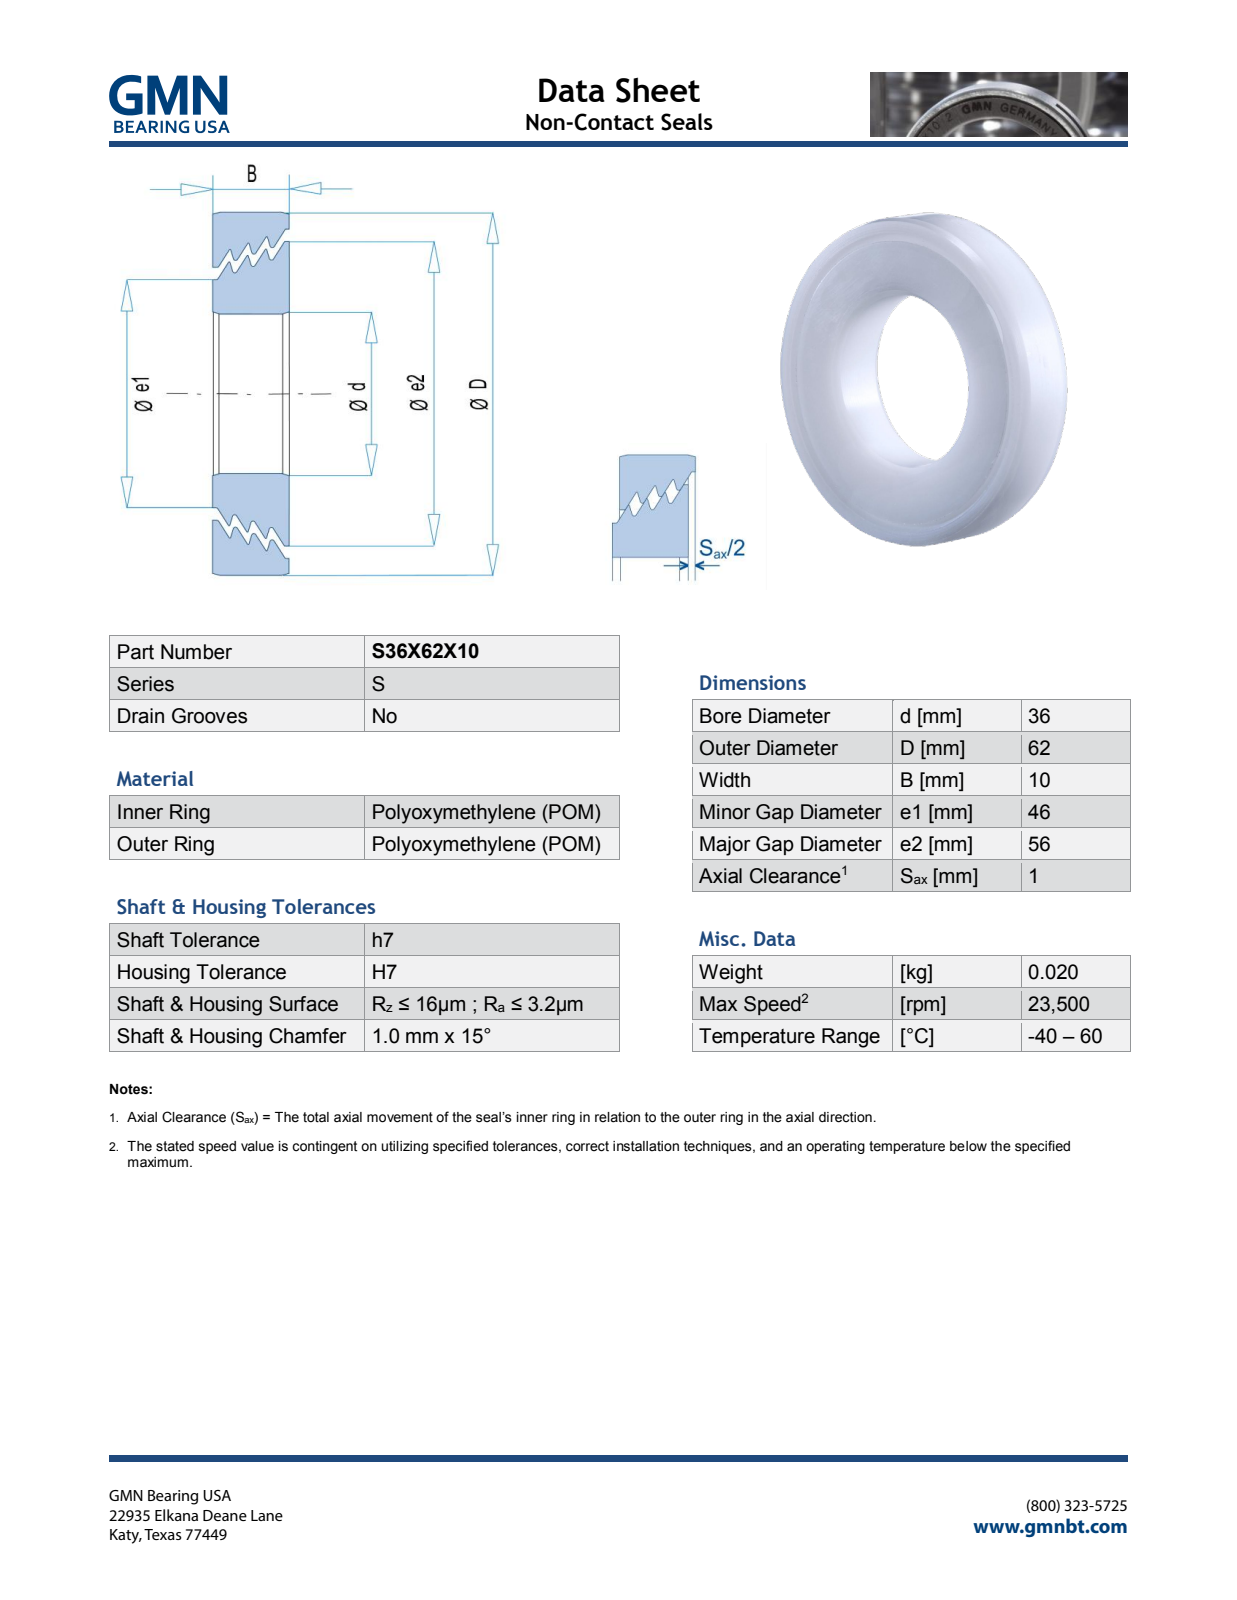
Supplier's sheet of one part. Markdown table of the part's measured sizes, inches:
| quantity | value |
| --- | --- |
| part name | S36X62X10_PRT |
| STEP written by | PRO/ENGINEER BY PARAMETRIC TECHNOLOGY CORPORATION, 2013150 (AUTOMOTIVE_DESIGN) |
| units | inches |
| bodies | 2 solids, 704 faces (624 planar, 12 cylindrical, 68 other) |
| overall size | 2.441 × 2.441 × 0.396 |
| volume | 1.135 in³ |
| surface area | 20.78 in² |
| round holes (diameter × count) | 1.417 × 1, 1.875 × 1, 2.269 × 1 |
| round bosses / shafts (diameter × count) | 2.441 × 1, 2.205 × 1, 1.811 × 1 |
| main face-to-face distances | 0.394, 0.396, 0.013, 0.014, 0.107, 0.094, 0.081, 0.094, 0.048, 0.012 |
